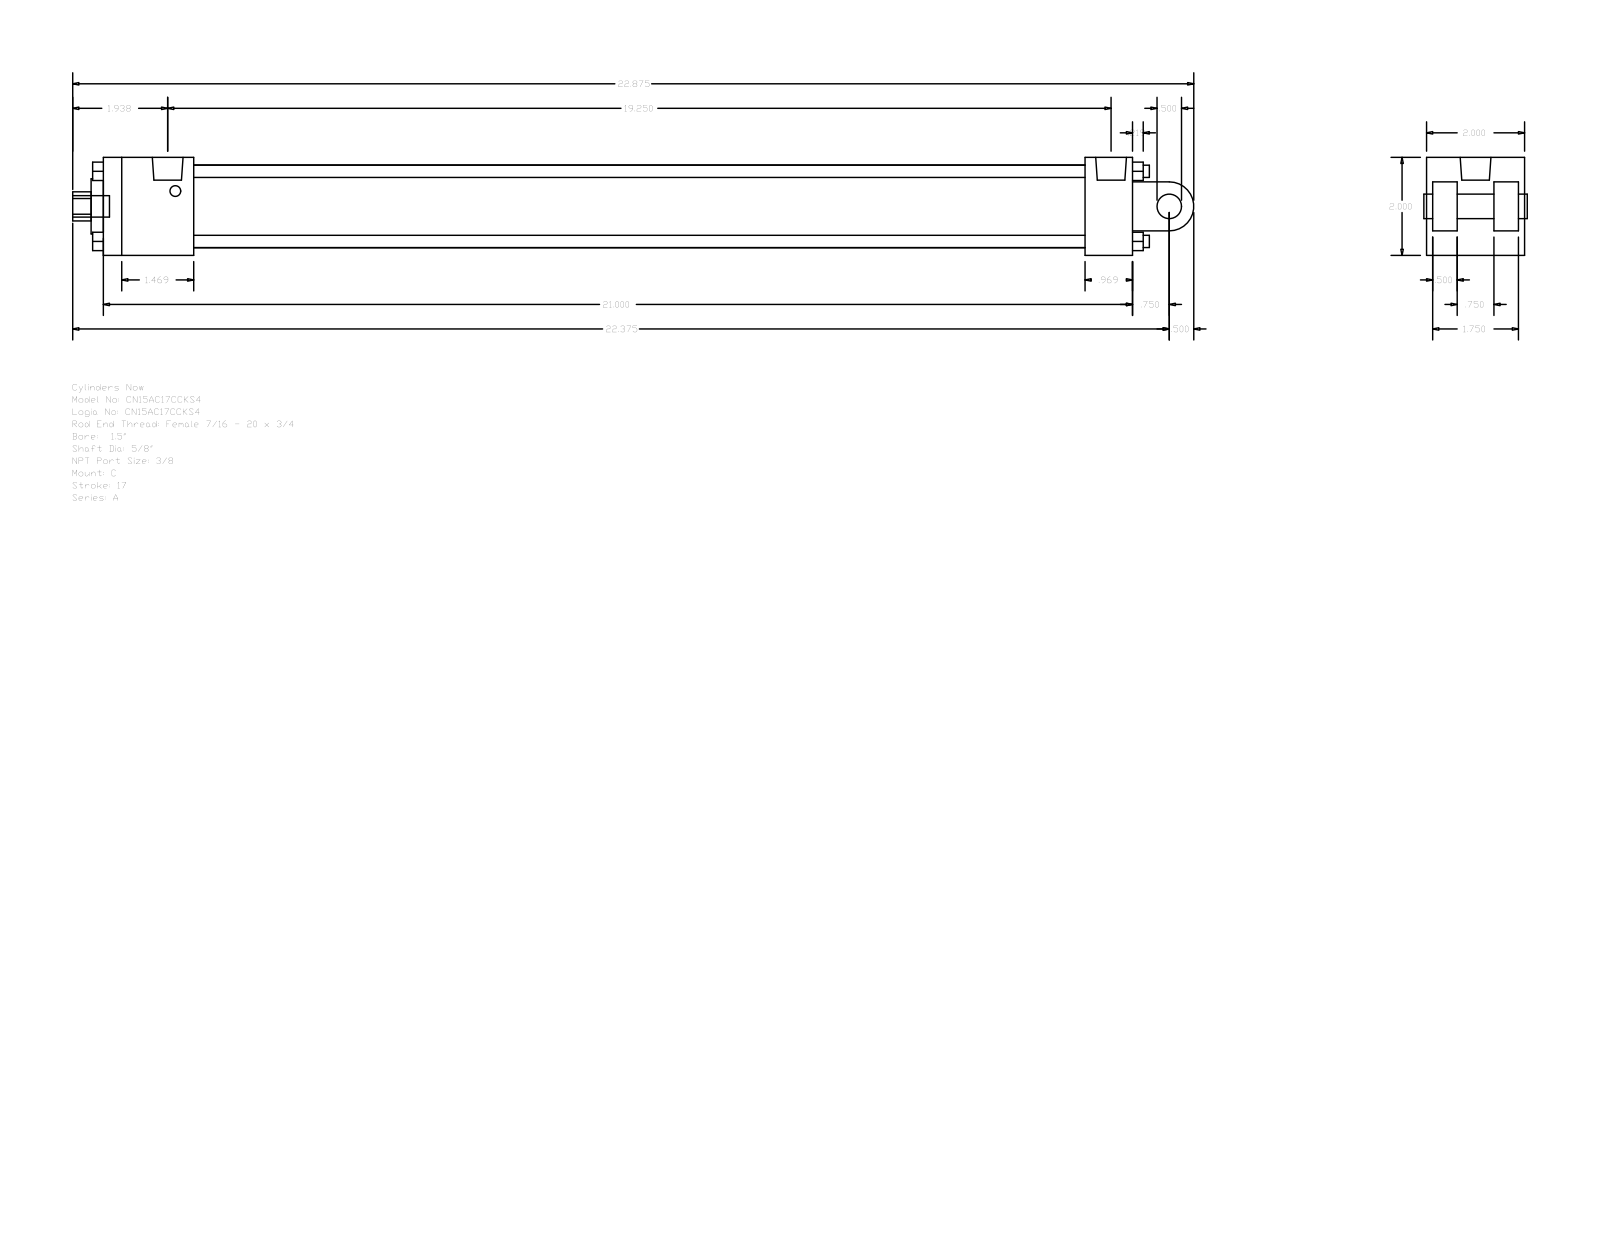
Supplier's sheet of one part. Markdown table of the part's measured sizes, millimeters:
| quantity | value |
| --- | --- |
| part name | A_C__0150_0.625 |
| STEP written by | GSSL Pune (CONFIG_CONTROL_DESIGN) |
| units | millimeters |
| bodies | 0 solids, 135 faces (102 planar, 33 cylindrical, 0 other) |
| overall size | 581.02 × 50.8 × 50.8 |
| round holes (diameter × count) | 5.56 × 2, 15.88 × 1, 15.93 × 1, 28.57 × 1, 42.93 × 1 |
| round bosses / shafts (diameter × count) | 6.35 × 4, 5.56 × 2, 15.93 × 1, 12.7 × 1, 11.11 × 1 |
| partial cylindrical surfaces (radius × count) | 7.54 × 1, 12.7 × 1 |
| main face-to-face distances | 50.8, 12.7, 533.39, 3.17, 47.63, 15.87, 34.93, 31.76, 508.79, 24.6 |
| hole center spacings | 3.97 |
